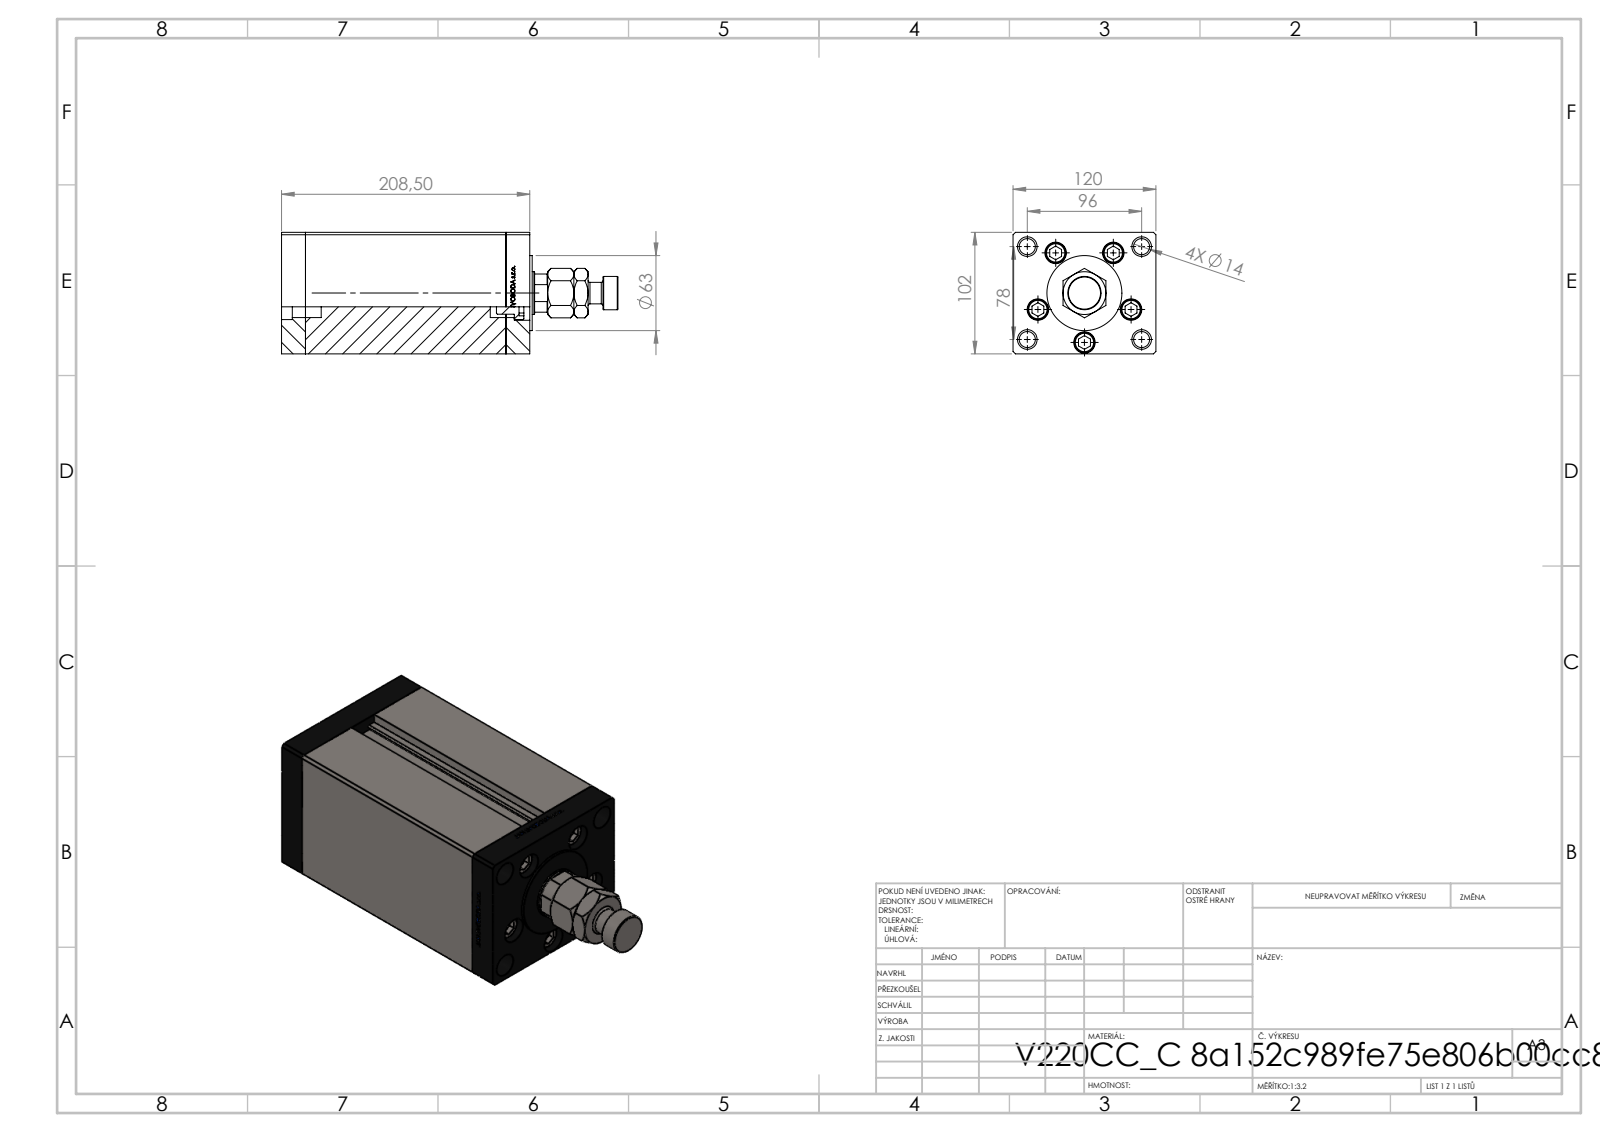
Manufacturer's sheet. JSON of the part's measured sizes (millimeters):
{"part_name": "ALLEN BOLT; V220C FRONT; V220C_VC_C; V220C_C MIDDLE (+2 more)", "step_written_by": "SolidWorks 2019 (CONFIG_CONTROL_DESIGN)", "units": "millimeters", "bodies": {"solids": 14, "faces": 1217, "planar": 558, "cylindrical": 165, "other": 494}, "overall_size": [282.5, 120, 102], "volume_mm3": 2190000, "surface_area_mm2": 307241, "round_holes": [[13.5, 9], [18, 5], [12, 4], [16.5, 4], [17, 1], [25.5, 1], [36, 1]], "round_bosses_or_shafts": [[8, 5], [17, 4], [63, 1], [28, 1], [18, 1]], "partial_cylinders_radius": [[0.93, 2], [17.5, 1]], "face_to_face_distances": [120, 102, 20, 168.5, 188.5, 34.25, 208.5, 174.25, 154.25, 14.25], "hole_center_spacings": [41.5, 61.85, 24.39, 26.69, 47.92, 48.07, 49.84, 53.57]}
